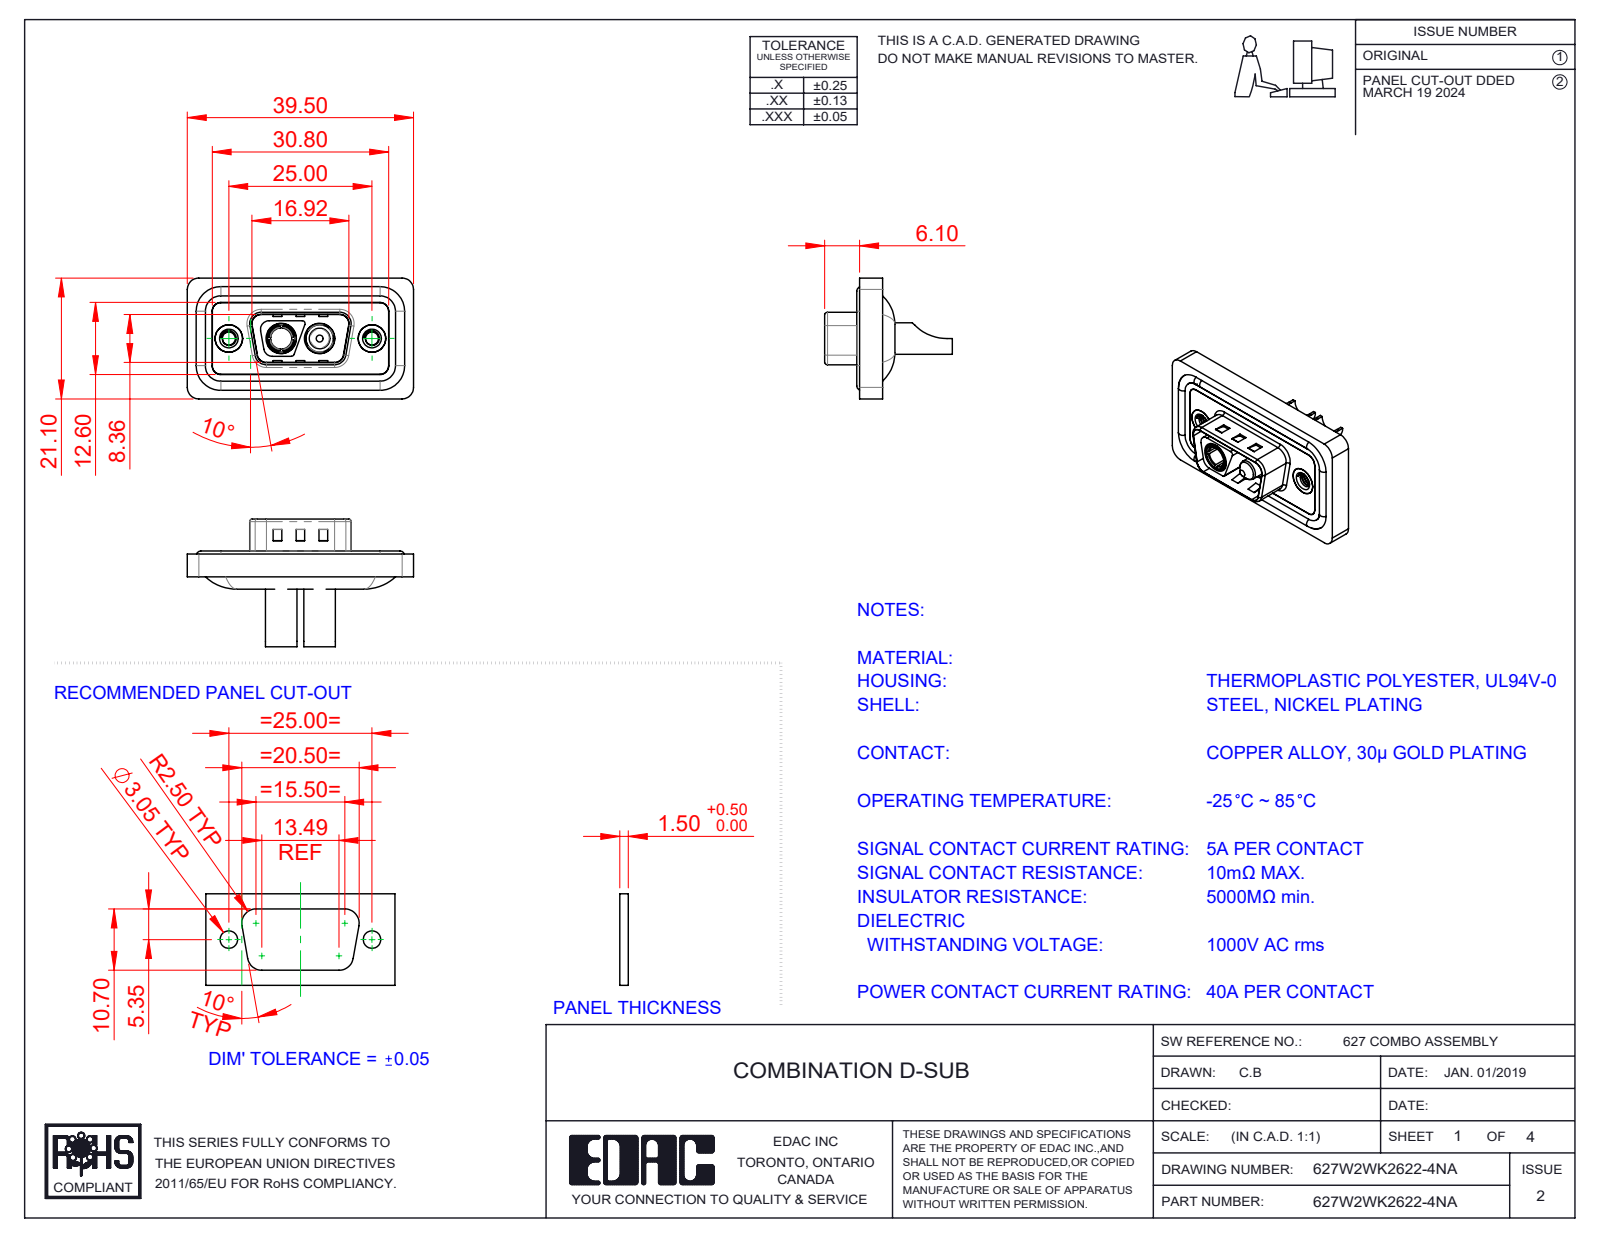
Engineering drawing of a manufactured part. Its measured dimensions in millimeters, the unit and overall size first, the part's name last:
Units: millimetres
Overall size (bounding box): 39.5 × 22.3 × 21.1
Round holes (diameter × count): ⌀2.26 ×2, ⌀4 ×2, ⌀4.6 ×2, ⌀4.8 ×2, ⌀4.85 ×2, ⌀5 ×2, ⌀5.3 ×2, ⌀3.7 ×1
Round bosses / shafts (diameter × count): ⌀1.6 ×4, ⌀5.5 ×2, ⌀5.2 ×2, ⌀4.9 ×2, ⌀4.75 ×2, ⌀3.75 ×2, ⌀4.96 ×1, ⌀3.6 ×1
Partial cylindrical surfaces — rounded edges, fillets, slot ends (radius × count): R1.5 ×24, R2 ×18, R0.5 ×10, R1.6 ×8, R0.25 ×4, R0.6 ×4, R0.65 ×4, R0.9 ×4
Main face-to-face distances: 0.4, 1.1, 2.9, 0.5, 3.1, 1.6, 2.5, 1.8, 3.2, 1.5
Hole centre spacings: 9.14, 15.86, 6.72, 25
Volume: 4 636 mm³ · Surface area: 7 620 mm²
Bodies: 11 solids, 540 faces (193 planar, 231 cylindrical, 116 other)
Part name (STEP PRODUCT): Power Socket_40A SC; 627Combo Shell Front_09 Contacts; Power Pin_40A SC; 627Combo Threaded Rivet_A (+4 more)
STEP written by: SolidWorks 2023 (CONFIG_CONTROL_DESIGN)
